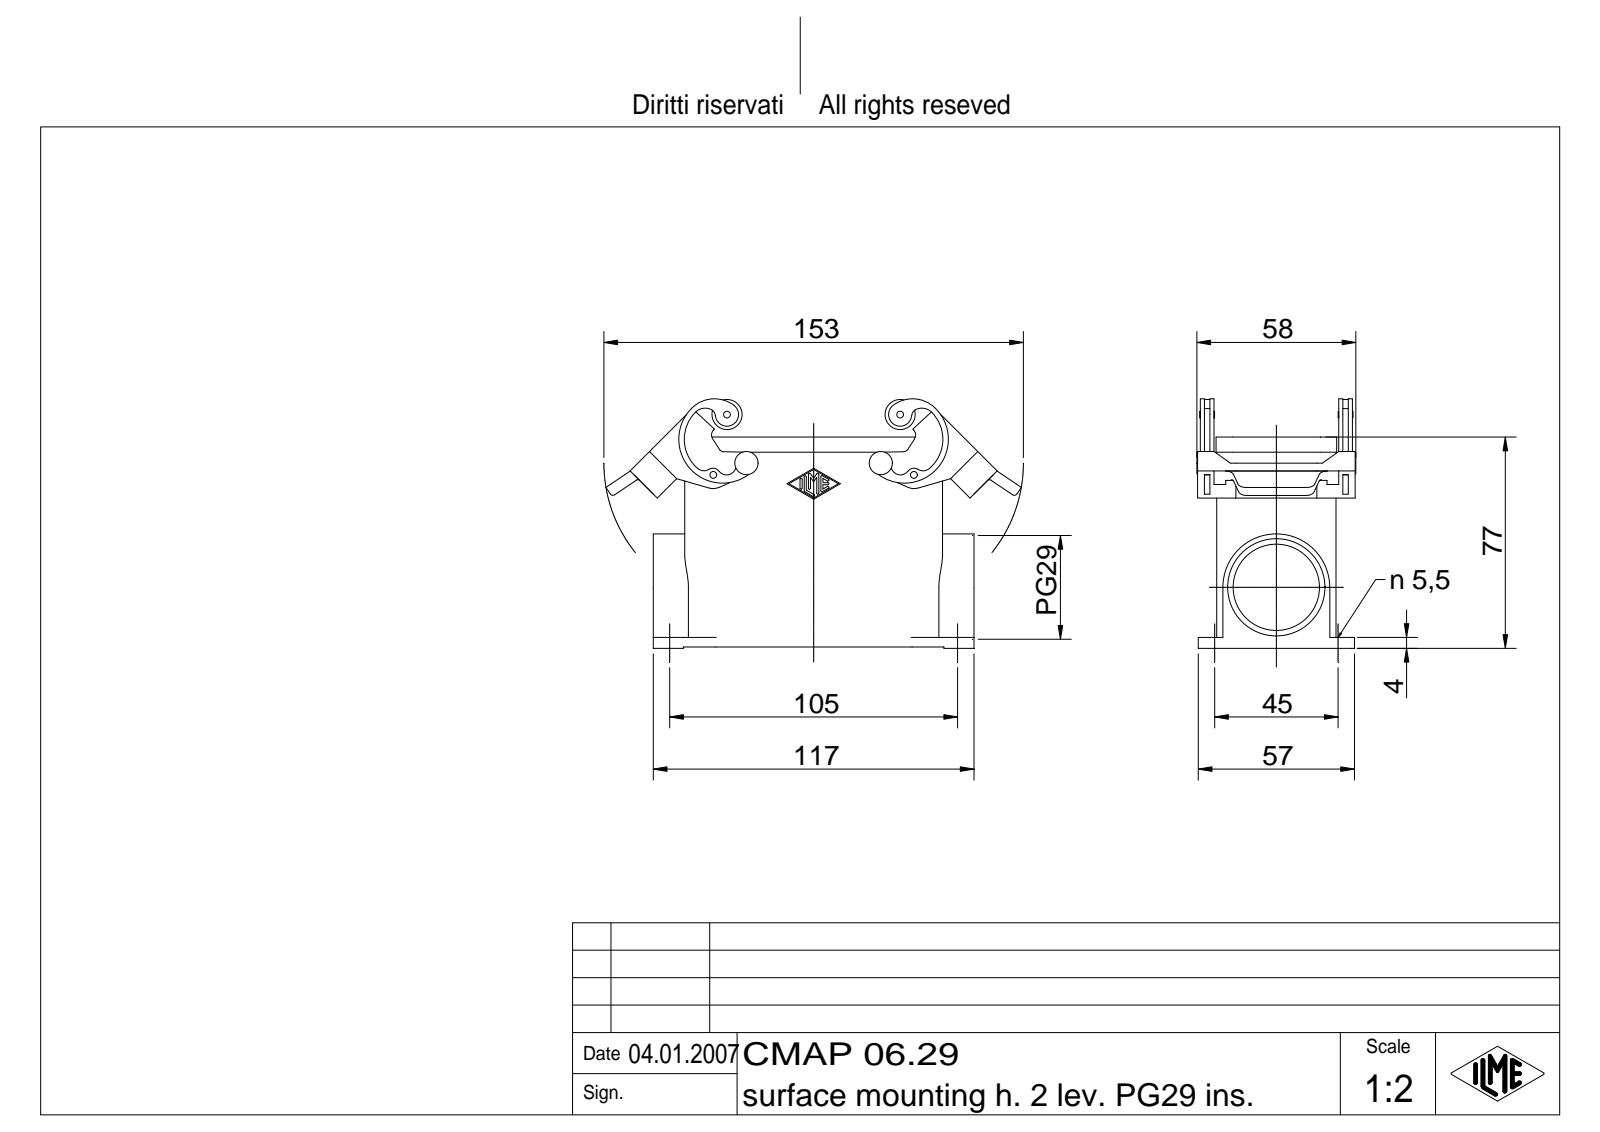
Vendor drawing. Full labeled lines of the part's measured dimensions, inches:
Part name (STEP PRODUCT): CMAP 06.29
STEP written by: Autodesk Inventor 7 (AUTOMOTIVE_DESIGN)
Units: inches
Bodies: 1 solid, 749 faces (191 planar, 205 cylindrical, 353 other)
Overall size (bounding box): 5.964 × 3.58 × 2.283
Volume: 7.421 in³ · Surface area: 108.1 in²
Round holes (diameter × count): ⌀0.079 ×4, ⌀0.217 ×4, ⌀0.098 ×2, ⌀1.239 ×1, ⌀1.397 ×1
Round bosses / shafts (diameter × count): ⌀0.433 ×2, ⌀0.197 ×2, ⌀0.118 ×2
Partial cylindrical surfaces — rounded edges, fillets, slot ends (radius × count): R0.039 ×20, R0.015 ×14, R0.118 ×12, R0.236 ×8, R0.098 ×6, R0.059 ×4, R0.079 ×4, R0.138 ×4
Main face-to-face distances: 0.118, 1.594, 1.713, 1.476, 0.138, 0.157, 0.03, 1.988, 1.604, 0.177
Hole centre spacings: 0.888, 1.772, 2.82, 4.134, 4.498, 2.486, 2.881
